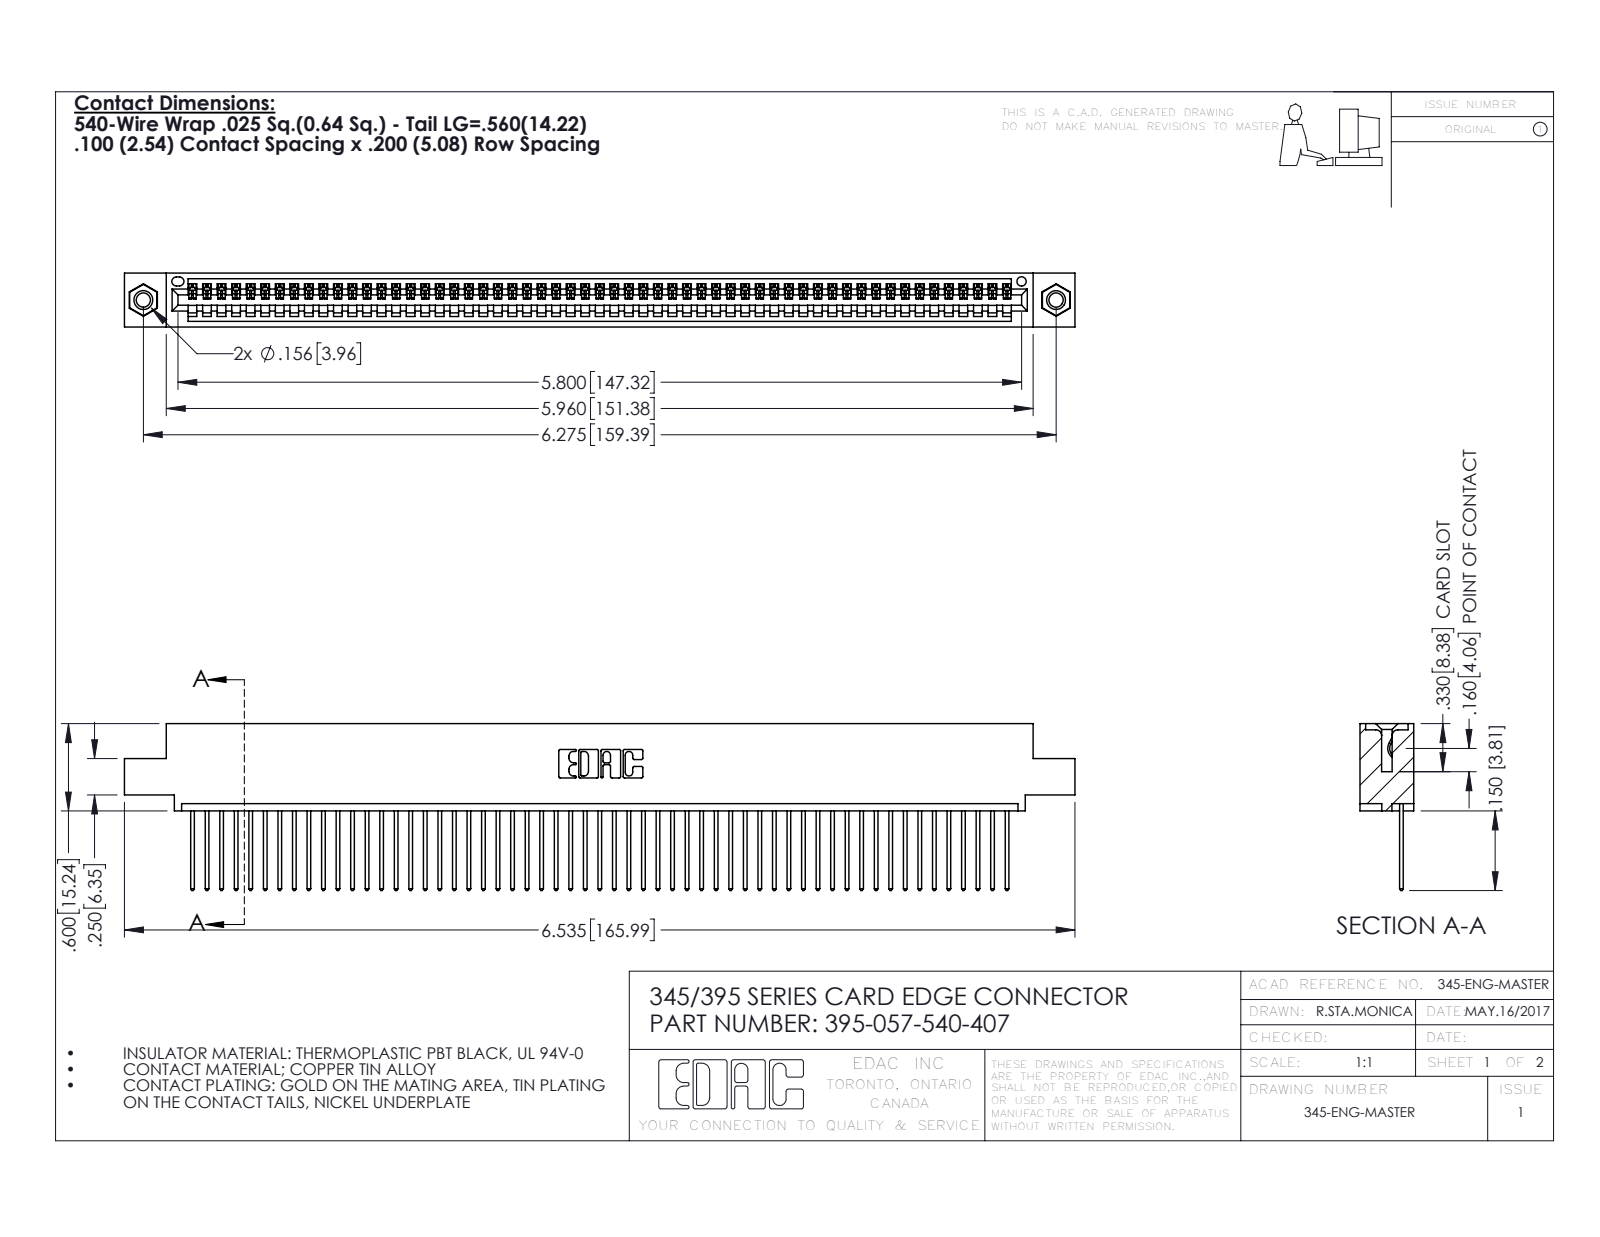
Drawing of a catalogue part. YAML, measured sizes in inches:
part_name: "345-292-001_345-293-140; 345 Part_0.110 Offset - 0.156 Dia-TI; 345-250-001_345-250-005-103; 395-057-540-407"
step_written_by: "SolidWorks 2016 (CONFIG_CONTROL_DESIGN)"
units: inches
bodies: {solids: 60, faces: 3496, planar: 2396, cylindrical: 1084, other: 16}
overall_size: [6.535, 1.147, 0.37]
volume: 0.969
surface_area: 34.06
round_holes:
  - {diameter: 0.098, count: 2}
  - {diameter: 0.125, count: 2}
  - {diameter: 0.156, count: 2}
  - {diameter: 0.064, count: 1}
round_bosses_or_shafts:
  - {diameter: 0.155, count: 2}
partial_cylinders:
  - {radius: 0.006, count: 114}
  - {radius: 0.01, count: 114}
  - {radius: 0.01, count: 22}
  - {radius: 0.007, count: 6}
  - {radius: 0.031, count: 6}
  - {radius: 0.026, count: 3}
  - {radius: 0.031, count: 2}
  - {radius: 0.04, count: 2}
face_to_face_distances: [0.072, 0.298, 0.37, 0.098, 0.272, 0.025, 0.2, 0.225, 0.149, 0.072]
hole_center_spacings: [0.27, 6.039, 6.275]
